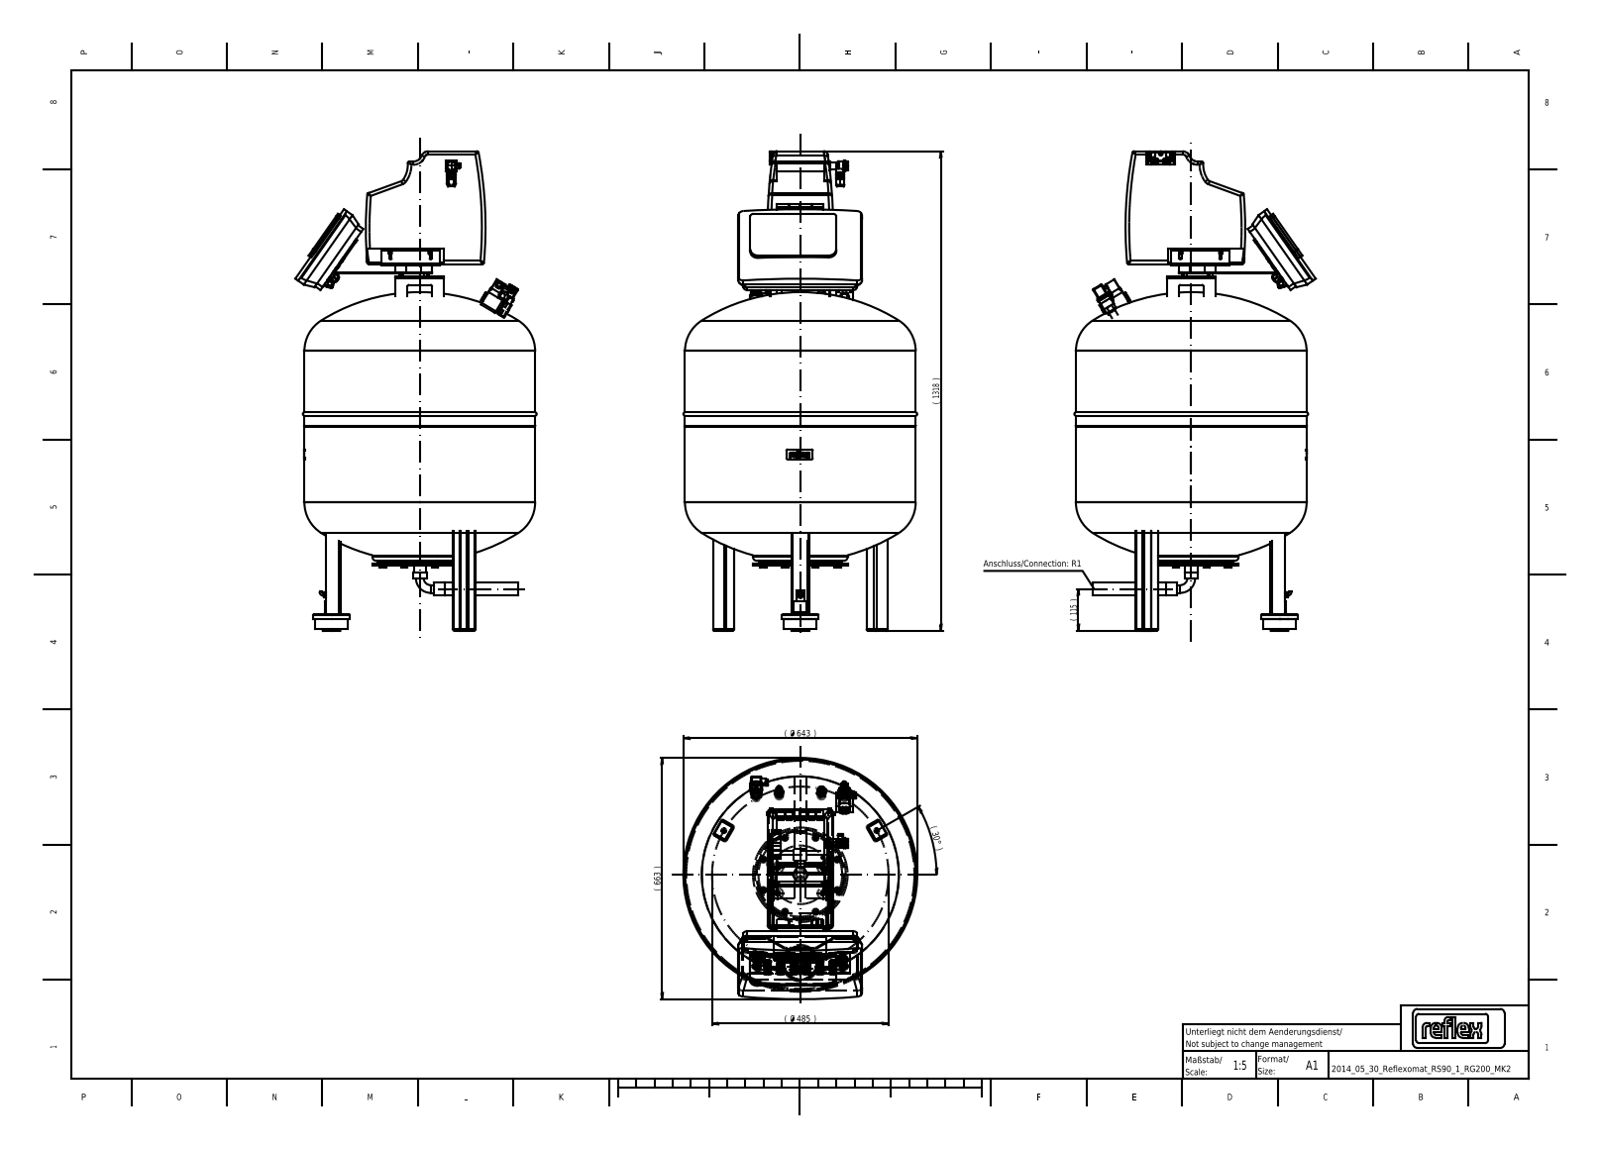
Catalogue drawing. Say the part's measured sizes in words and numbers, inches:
Its 3-D file was written by "CATIA V5 STEP AP214 (AUTOMOTIVE_DESIGN)". It is 41 solids with 2877 faces: 1967 planar, 548 cylindrical and 362 other. Overall it measures 51.89 by 26.115 by 25.307 inches. Its volume is 13 450 cubic inches and its surface area 7 406 square inches. Round holes: 8 of diameter 0.323, 8 of diameter 0.413, 7 of diameter 0.669, 4 of diameter 0.217, 4 of diameter 0.354, 2 of diameter 0.394, 2 of diameter 0.528, 1 of diameter 0.079, 1 of diameter 0.256, 1 of diameter 0.276, 1 of diameter 0.551, 1 of diameter 0.787. Round bosses or shafts: 10 of diameter 0.394, 8 of diameter 0.748, 8 of diameter 0.63, 8 of diameter 0.315, 7 of diameter 0.689, 4 of diameter 1.181, 3 of diameter 0.839, 3 of diameter 0.78. Partial cylindrical surfaces (rounded edges, fillets, slot ends): 31 of radius 0.098, 23 of radius 0.197, 14 of radius 0.315, 11 of radius 0.394, 10 of radius 0.039, 6 of radius 0.118, 4 of radius 0.155, 4 of radius 0.177. The main face-to-face distances are 16.378, 0.157, 0.098, 0.866, 0.079, 6.575, 22.953, 1.87, 0.236, 6.811. The hole center spacings are 4.921, 1.417, 2.835, 4.927, 4.997, 5.043, 4.252, 5.64.
